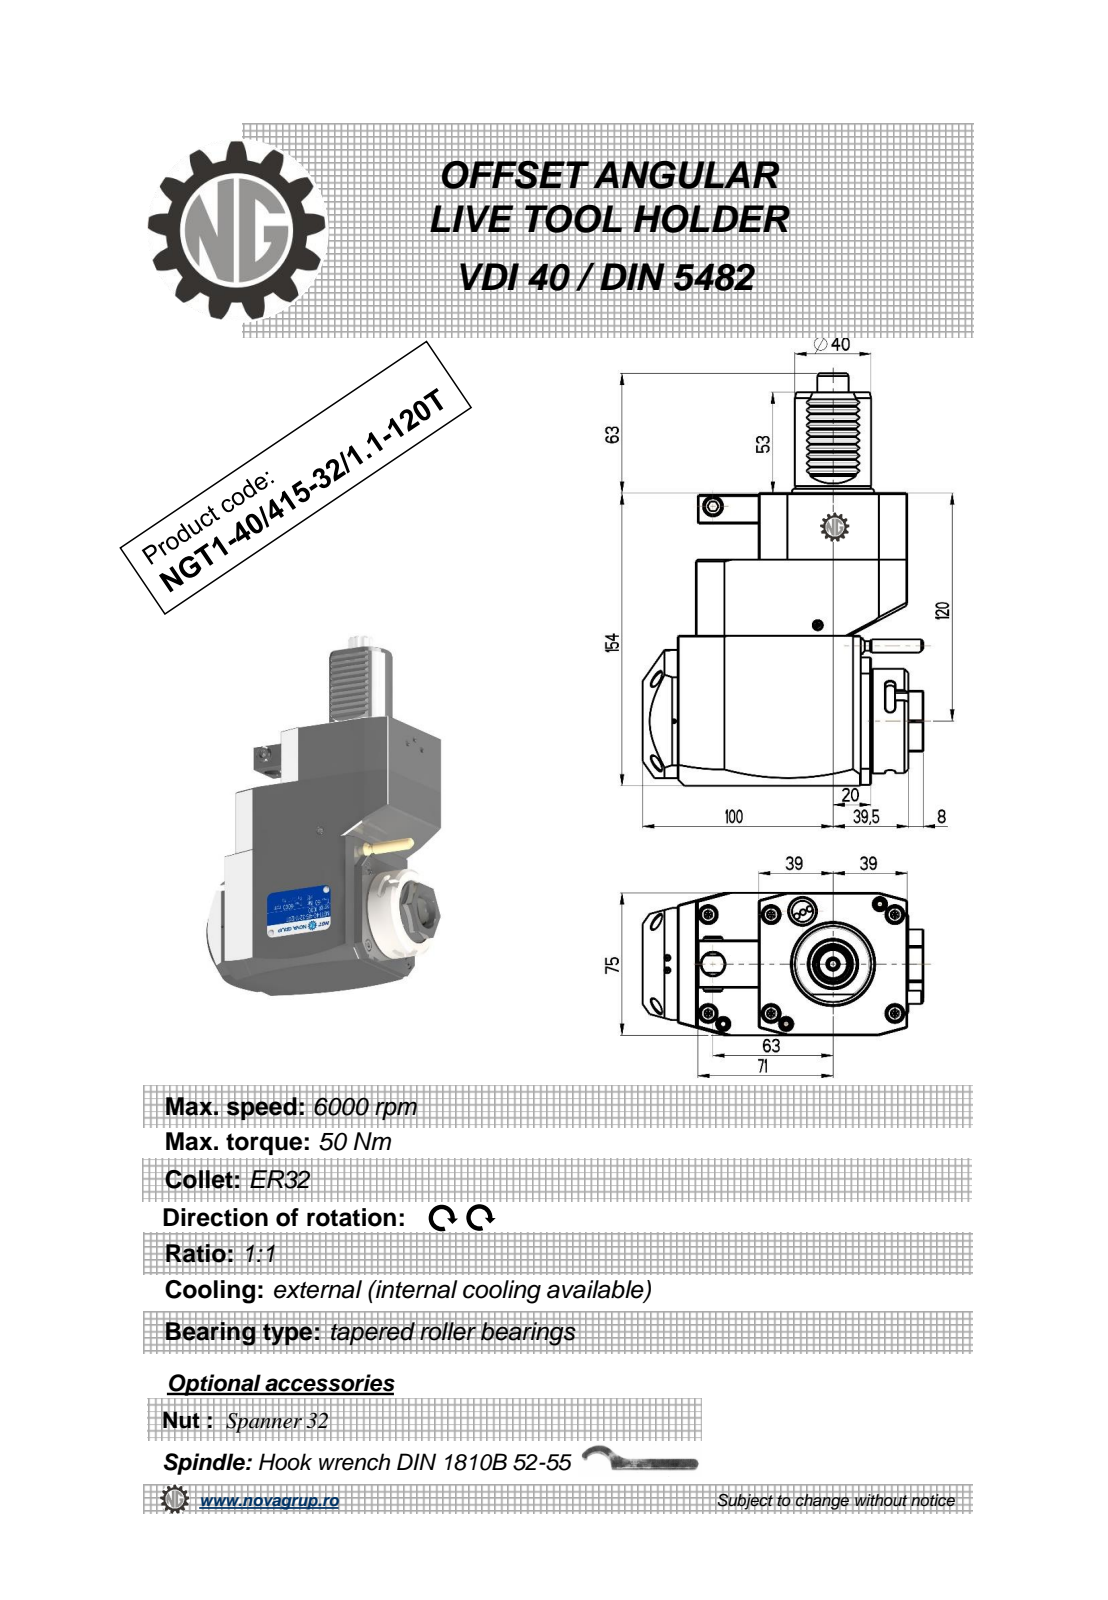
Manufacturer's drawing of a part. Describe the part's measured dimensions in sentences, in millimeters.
The part is named "NGT1_40_415_32_1_1_120T". Its 3-D file was written by "PRO/ENGINEER BY PARAMETRIC TECHNOLOGY CORPORATION, 2010280 (CONFIG_CONTROL_DESIGN)". It is 1 solid with 373 faces: 185 planar, 101 cylindrical and 87 other. Overall it measures 217 by 147.5 by 75 millimeters. Its volume is 1 263 000 cubic millimeters and its surface area 88 500 square millimeters. Round holes: 1 of diameter 2.5, 1 of diameter 3, 1 of diameter 4.2, 1 of diameter 5.3, 1 of diameter 9.5, 1 of diameter 12, 1 of diameter 23. Round bosses or shafts: 2 of diameter 8.96, 1 of diameter 55, 1 of diameter 48, 1 of diameter 40, 1 of diameter 10, 1 of diameter 7, 1 of diameter 5. Partial cylindrical surfaces (rounded edges, fillets, slot ends): 18 of radius 3.03, 10 of radius 0.3, 6 of radius 2.5, 2 of radius 180, 1 of radius 0.5, 1 of radius 4.25, 1 of radius 6.75, 1 of radius 8.25. The main face-to-face distances are 75, 154, 19, 59, 111, 92, 35, 119, 33, 0.5. The hole center spacings are 43.2, 63, 75.07, 112.5.
